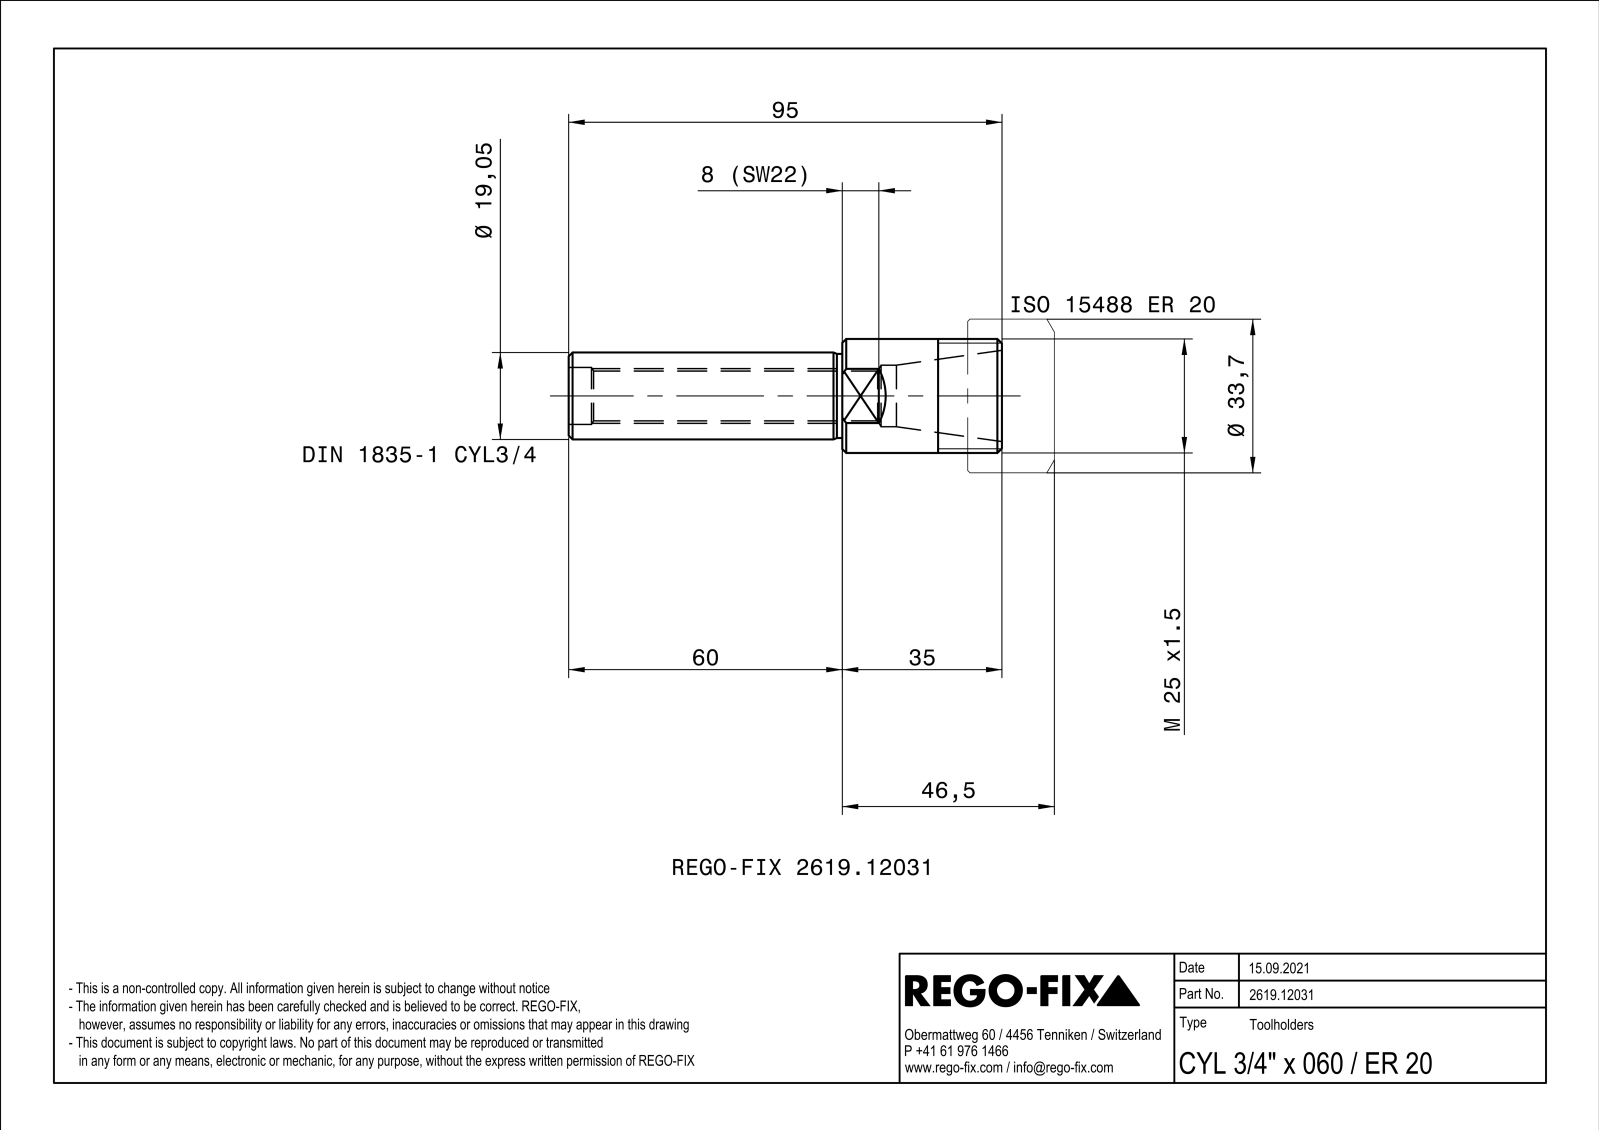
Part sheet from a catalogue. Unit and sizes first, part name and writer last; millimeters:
Units: millimetres
Overall size (bounding box): 85 × 25 × 25
Round holes (diameter × count): ⌀10.92 ×1, ⌀12.5 ×1, ⌀13.5 ×1
Round bosses / shafts (diameter × count): ⌀25 ×1, ⌀19.05 ×1, ⌀18.65 ×1
Main face-to-face distances: 22, 25, 85, 60, 5.09
Volume: 17 766 mm³ · Surface area: 9 382 mm²
Bodies: 1 solid, 27 faces (9 planar, 7 cylindrical, 11 other)
Part name (STEP PRODUCT): NOCUT
STEP written by: SIEMENS PLM Software Solid Edge ST10 (AUTOMOTIVE_DESIGN)
